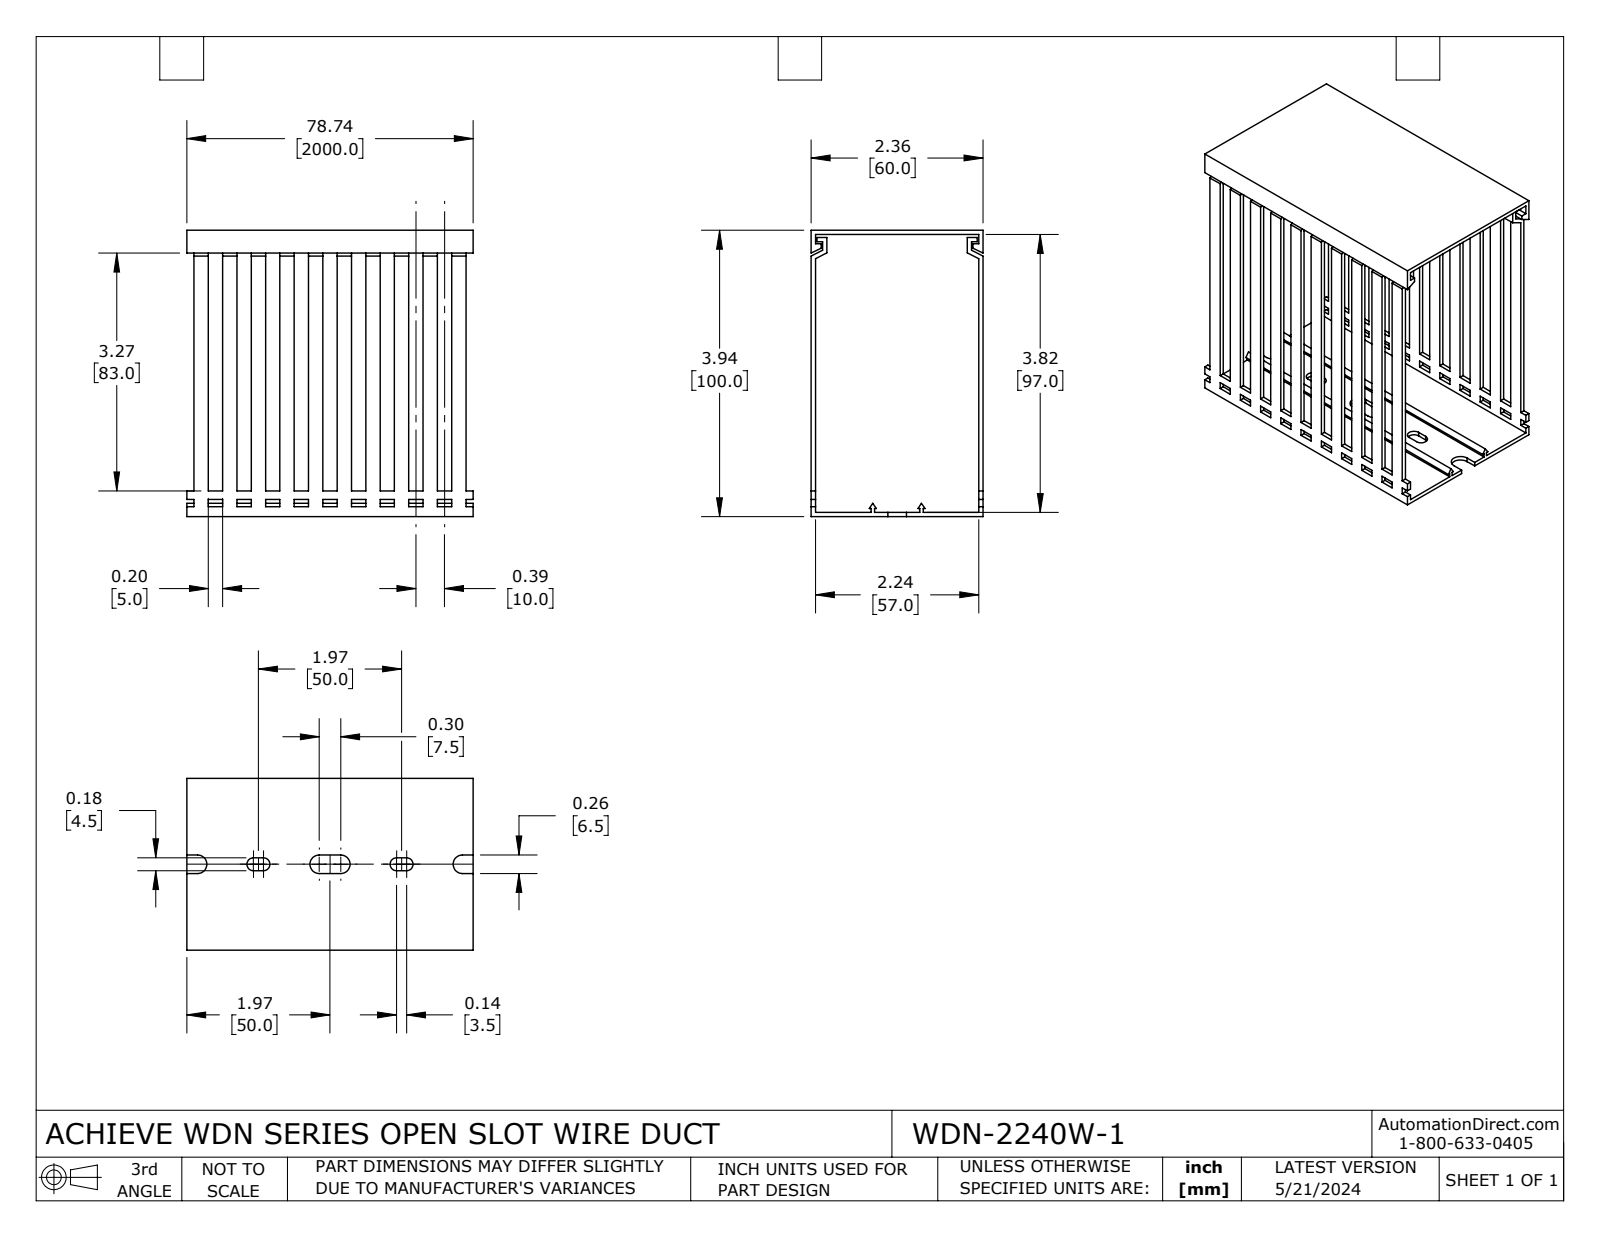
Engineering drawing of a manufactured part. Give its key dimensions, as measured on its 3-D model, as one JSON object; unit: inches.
{"part_name": "WDN-2240W-1", "step_written_by": "SolidWorks 2023 (CONFIG_CONTROL_DESIGN)", "units": "inches", "bodies": {"solids": 2, "faces": 350, "planar": 338, "cylindrical": 12, "other": 0}, "overall_size": [3.937, 3.937, 2.362], "volume_in3": 2.251, "surface_area_in2": 87.48, "partial_cylinders_radius": [[0.089, 4], [0.128, 4]], "face_to_face_distances": [0.059, 3.878, 2.303, 2.362, 3.937, 0.197, 3.819, 0.394, 2.244, 0.591]}
